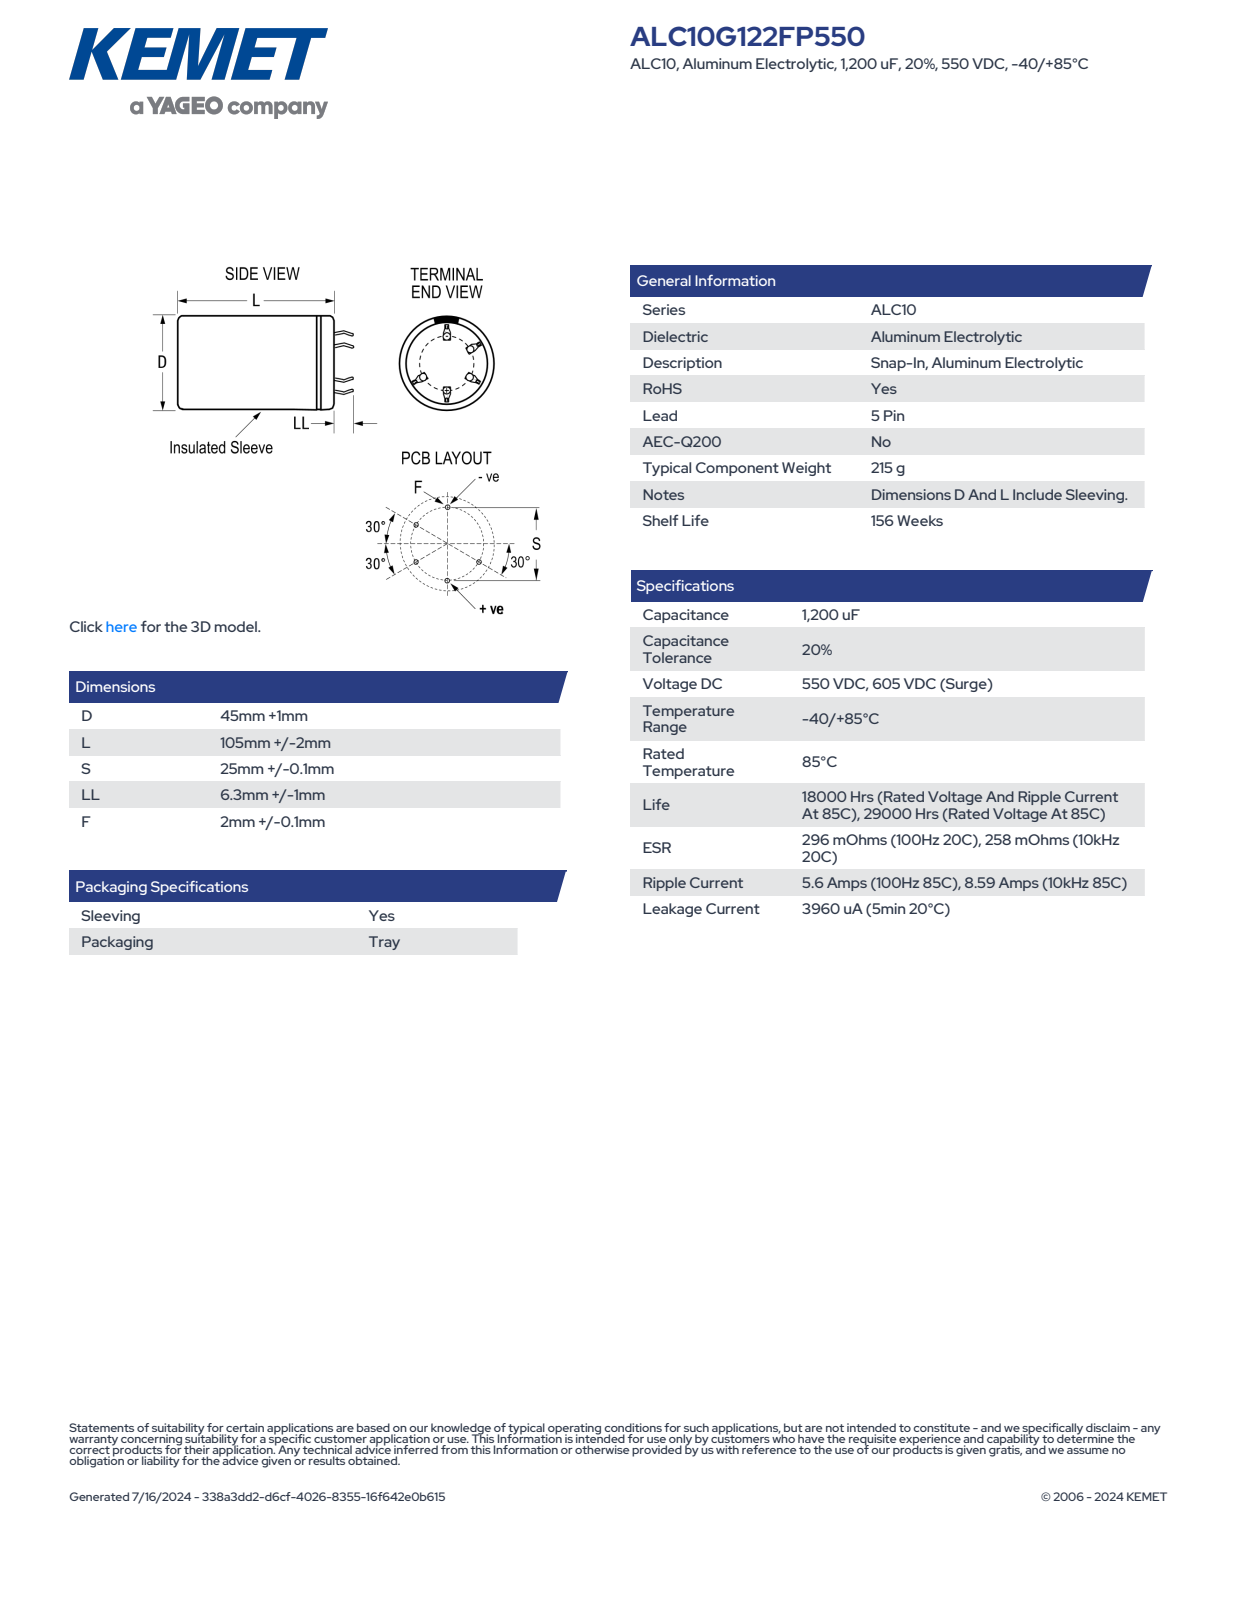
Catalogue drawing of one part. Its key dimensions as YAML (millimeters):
part_name: "CARS_K5P_45X105_D46L107S25LL7.3F2.1"
step_written_by: "SolidWorks 2014 (AUTOMOTIVE_DESIGN)"
units: millimeters
bodies: {solids: 1, faces: 148, planar: 94, cylindrical: 15, other: 39}
overall_size: [114.29, 46, 46]
volume: 176731
surface_area: 18826
round_holes:
  - {diameter: 40.7, count: 1}
round_bosses_or_shafts:
  - {diameter: 46, count: 1}
partial_cylinders:
  - {radius: 22.99, count: 1}
face_to_face_distances: [106.99, 107.49, 0.5, 0.6, 0.54, 0.75, 1.35, 25.37, 0.53, 2.1]
